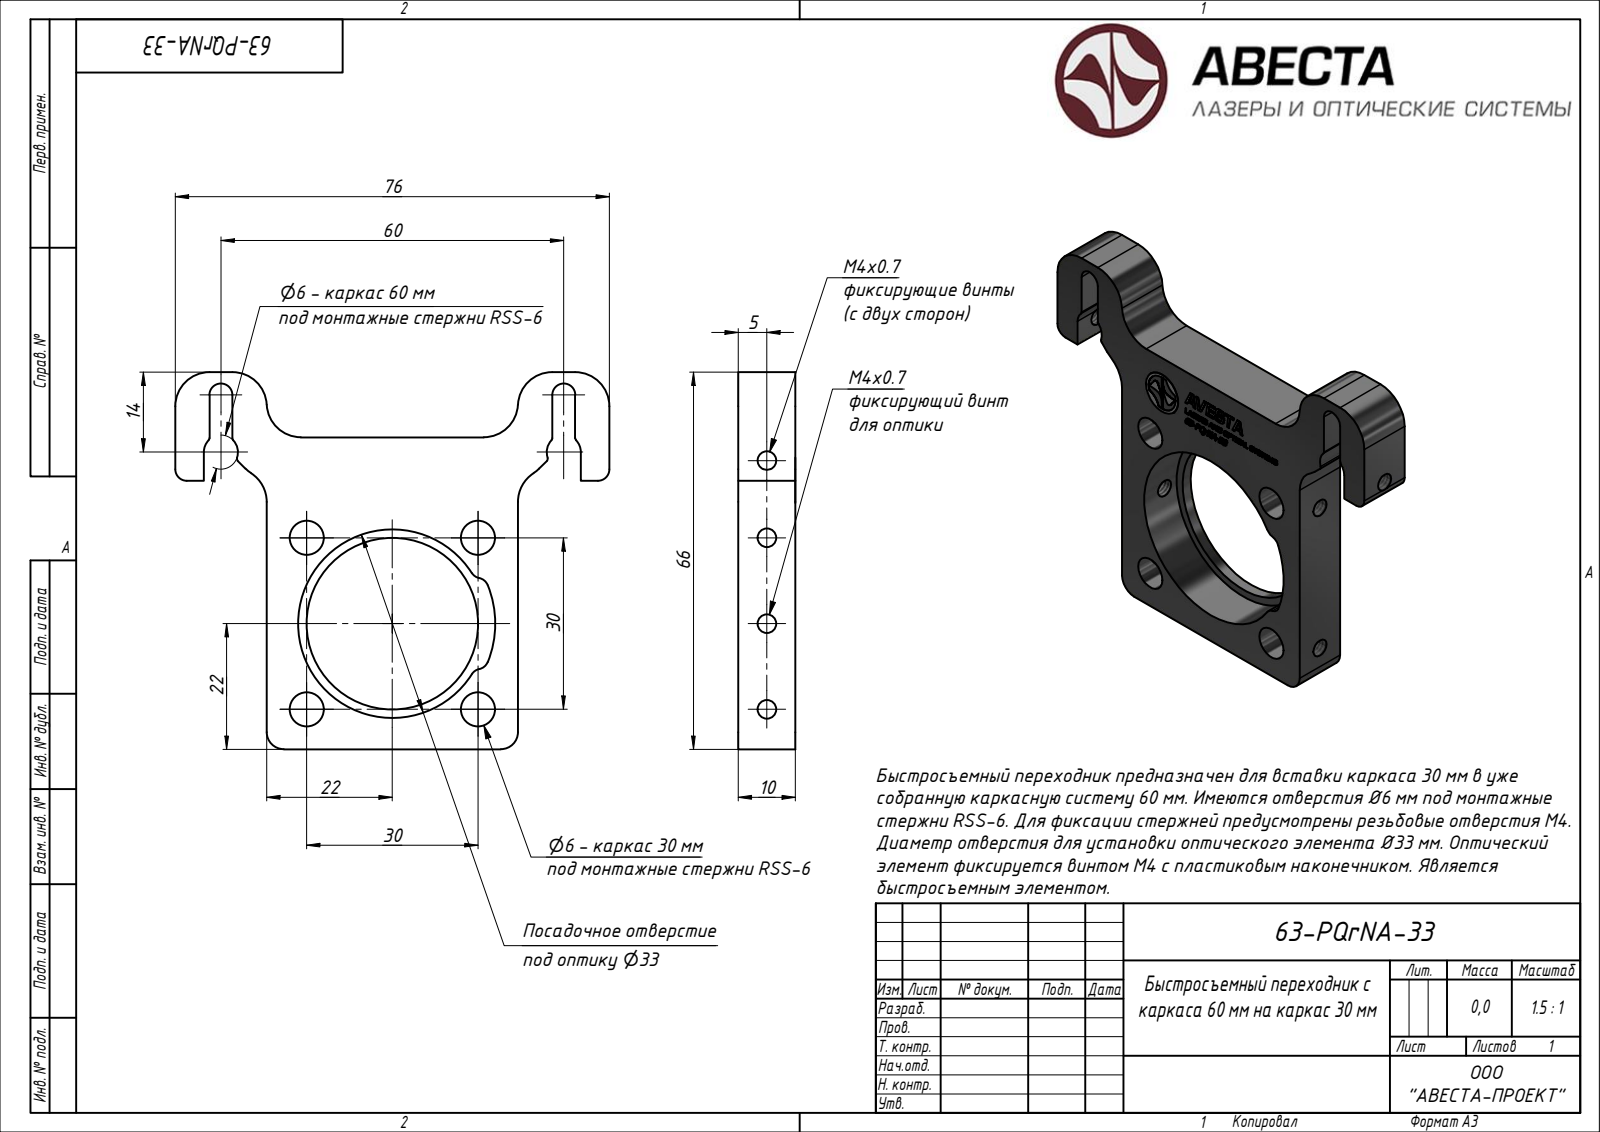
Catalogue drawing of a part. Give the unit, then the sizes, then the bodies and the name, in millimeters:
Units: millimetres
Overall size (bounding box): 76 × 66 × 10
Round holes (diameter × count): ⌀3.24 ×4, ⌀6 ×4, ⌀30 ×1, ⌀33 ×1
Round bosses / shafts (diameter × count): ⌀7.95 ×1
Partial cylindrical surfaces — rounded edges, fillets, slot ends (radius × count): R0.39 ×10, R6 ×10, R2 ×8, R0.12 ×6, R0.17 ×6, R0.21 ×6, R0.5 ×6, R0.1 ×5
Main face-to-face distances: 10, 44, 60, 54.58, 6, 66, 16, 8, 2, 5
Hole centre spacings: 30, 21.21, 15, 42.43, 13.5, 28.5, 43.5
Volume: 18 349 mm³ · Surface area: 9 429 mm²
Bodies: 1 solid, 825 faces (363 planar, 357 cylindrical, 105 other)
STEP written by: Rhino 7.34 (AUTOMOTIVE_DESIGN)
